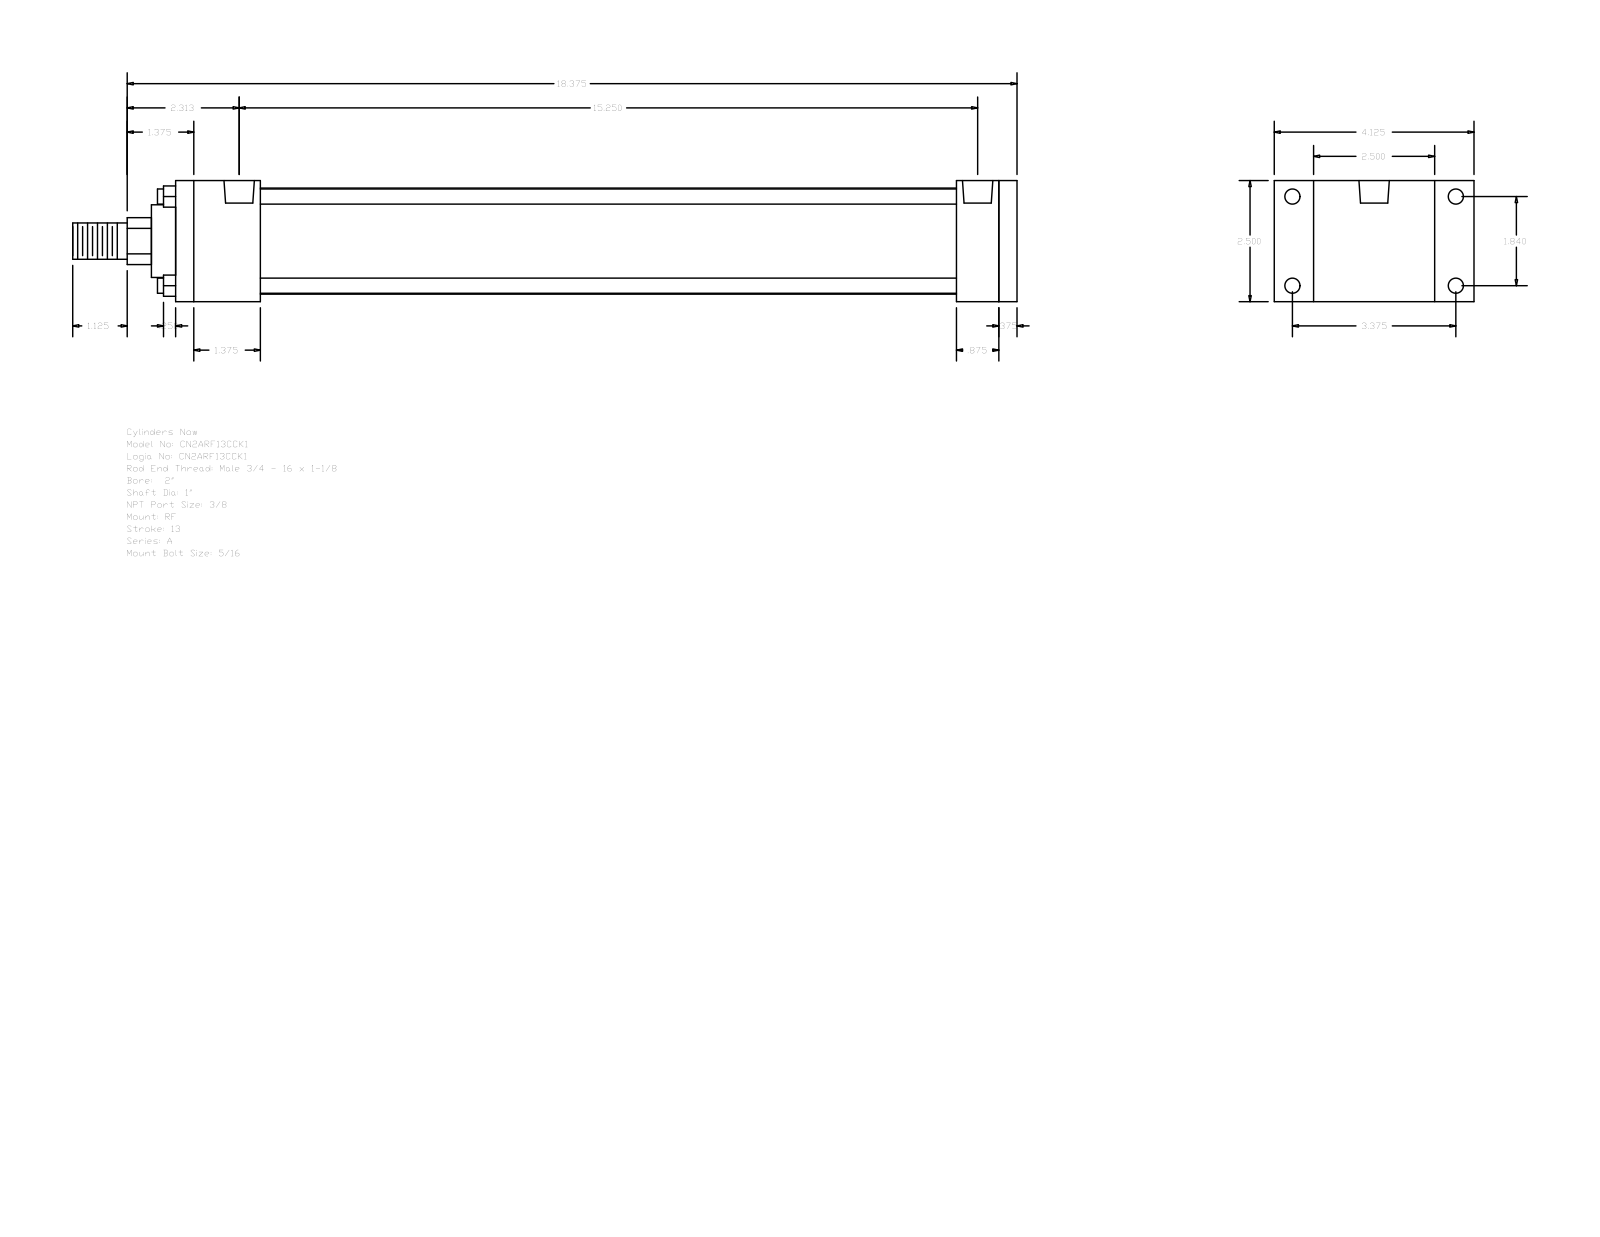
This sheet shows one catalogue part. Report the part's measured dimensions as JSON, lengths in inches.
{"part_name": "A_RF__0200_1", "step_written_by": "GSSL Pune (CONFIG_CONTROL_DESIGN)", "units": "inches", "bodies": {"solids": 0, "faces": 92, "planar": 64, "cylindrical": 28, "other": 0}, "overall_size": [19.5, 4.125, 2.5], "round_holes": [[0.219, 4], [0.313, 4], [0.627, 2]], "round_bosses_or_shafts": [[0.313, 4], [2.19, 1], [1.5, 1], [1, 1], [0.75, 1]], "partial_cylinders_radius": [[0.484, 1]], "face_to_face_distances": [2.5, 0.375, 17.375, 17, 1.75, 0.813, 15.25, 15.625, 16.125, 14.375], "hole_center_spacings": [1.84, 3.375, 3.844, 15.031, 0.063, 0.157, 15.093, 15.187]}
